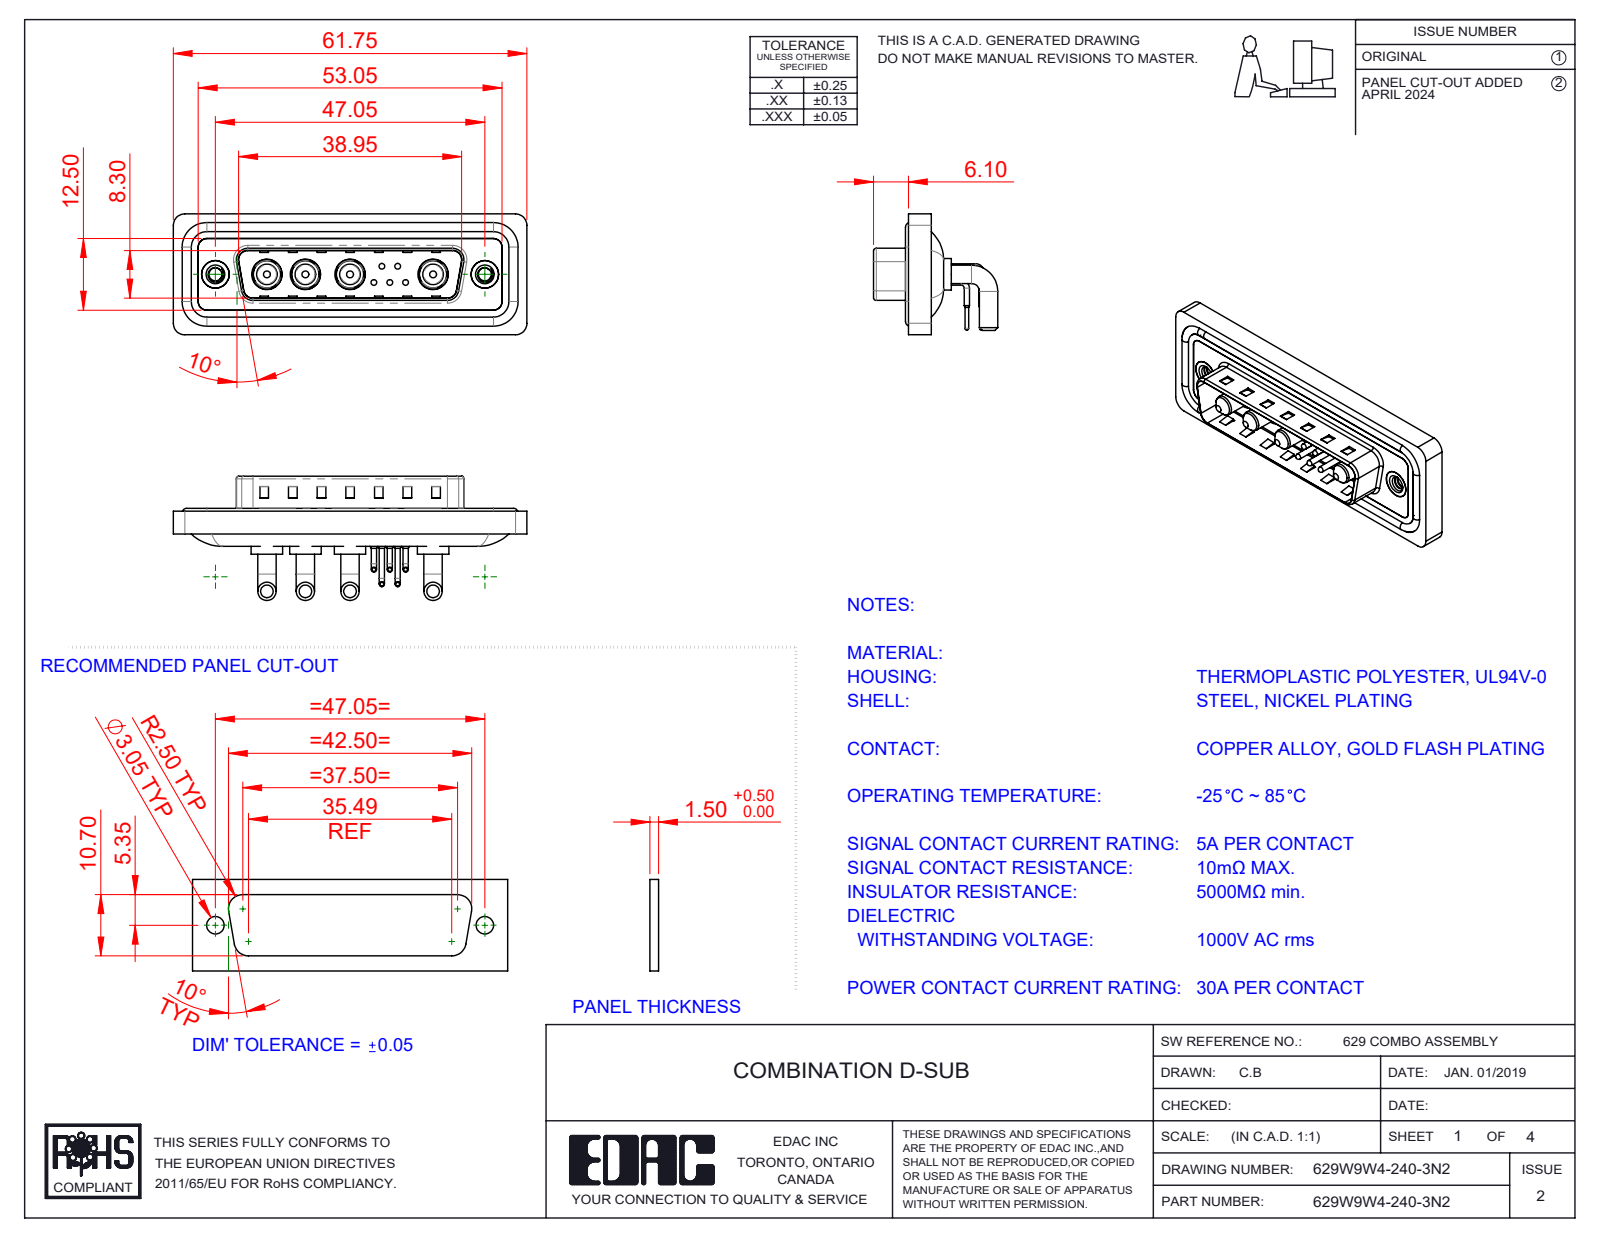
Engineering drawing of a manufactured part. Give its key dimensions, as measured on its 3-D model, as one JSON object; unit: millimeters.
{"part_name": "629Combo Shell Front_25 Contacts; 629W9W4-240-3N2; 629Combo Housing_9W4; 629Combo Contact Row 1 (+5 more)", "step_written_by": "SolidWorks 2023 (CONFIG_CONTROL_DESIGN)", "units": "millimeters", "bodies": {"solids": 20, "faces": 1205, "planar": 569, "cylindrical": 452, "other": 184}, "overall_size": [61.75, 21.7, 21.1], "volume_mm3": 7827, "surface_area_mm2": 12451, "round_holes": [[0.75, 5], [1.6, 5], [2, 5], [4.85, 4], [5.3, 4], [2.26, 2], [4, 2], [4.8, 2], [5, 2]], "round_bosses_or_shafts": [[0.9, 10], [3.2, 8], [1.5, 5], [1, 5], [0.65, 5], [5.5, 4], [5.2, 4], [4.75, 4]], "partial_cylinders_radius": [[1.5, 18], [2, 18], [0.5, 8], [1.6, 8], [1.01, 5], [0.25, 4], [0.6, 4], [0.65, 4]], "face_to_face_distances": [0.4, 2.9, 0.8, 4.1, 1.1, 4.5, 2.1, 1.6, 3.1, 1.5], "hole_center_spacings": [3.16, 2.77, 5.04, 14.5, 2.78, 4.4, 4.41, 5]}
